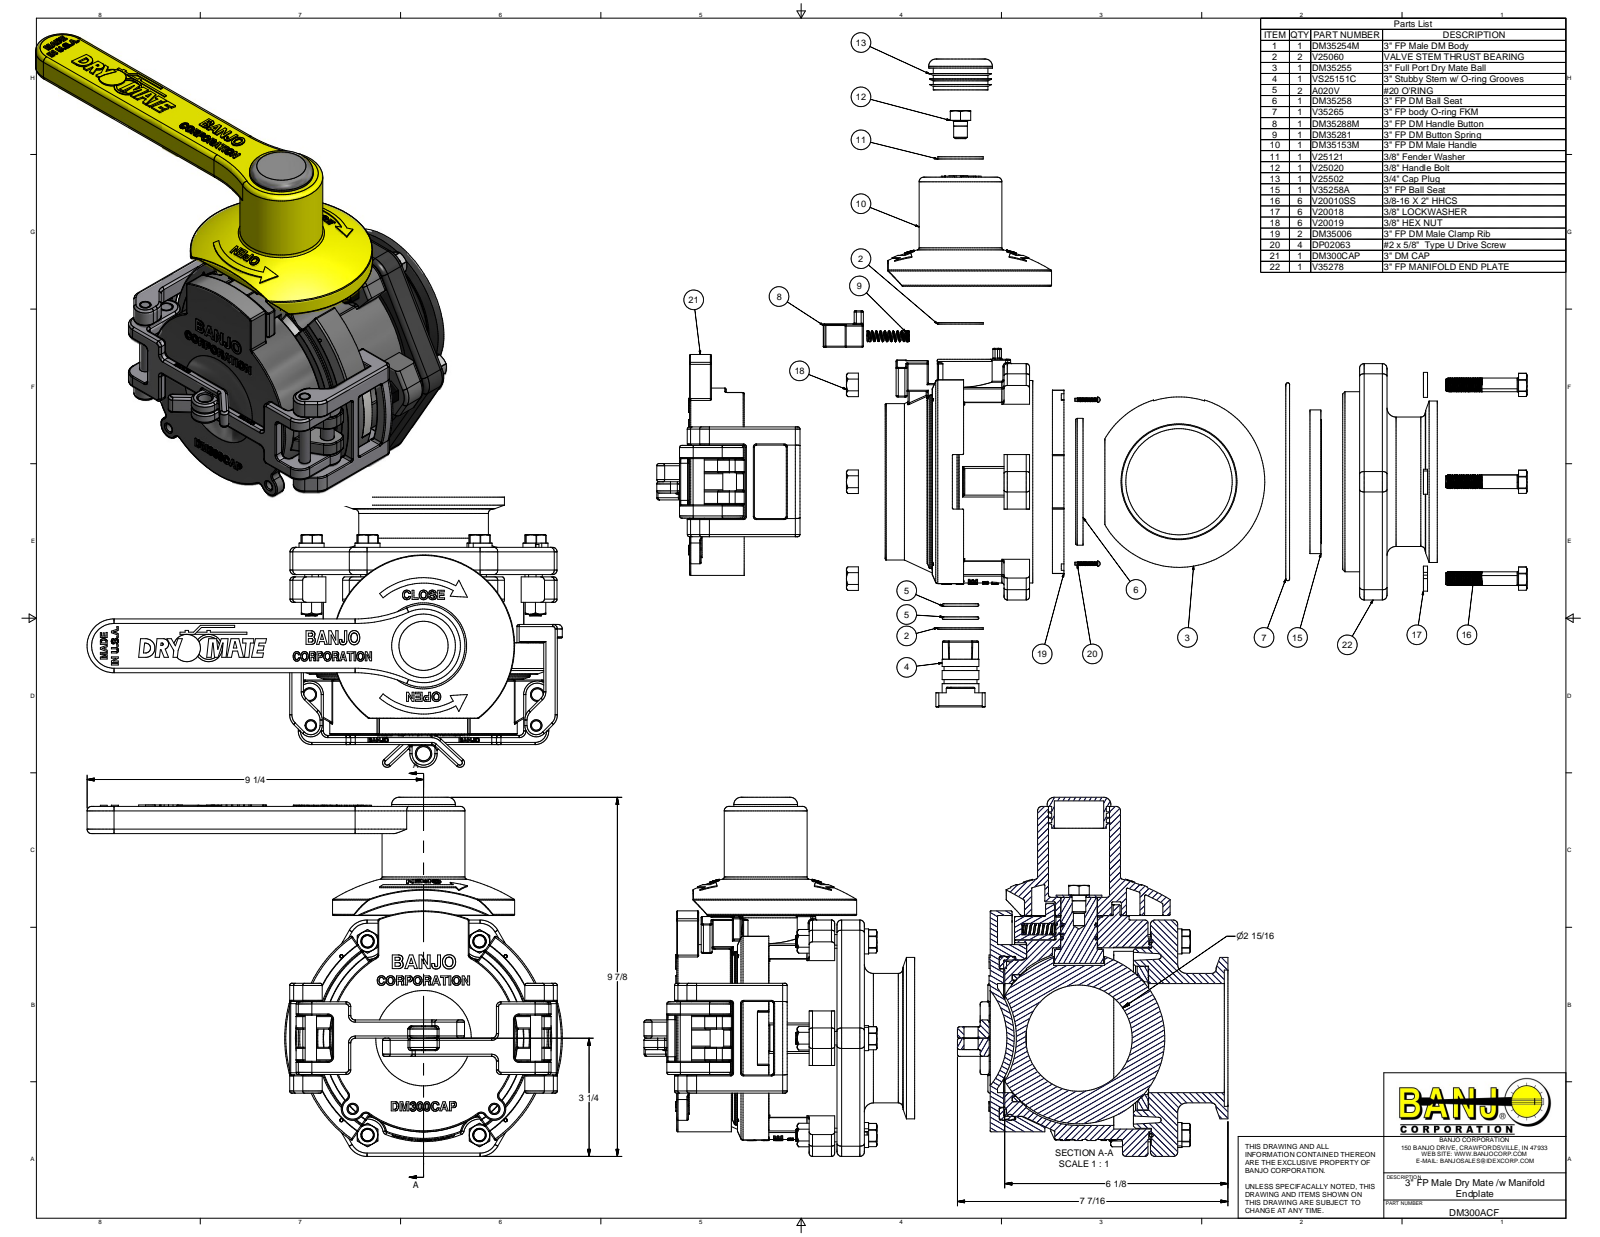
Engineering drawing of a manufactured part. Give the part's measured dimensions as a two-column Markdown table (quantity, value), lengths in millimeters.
| quantity | value |
| --- | --- |
| part name | DM35254MX; DM35254M; V35278X; V35278 (+8 more) |
| STEP written by | Autodesk Inventor 2014 (AUTOMOTIVE_DESIGN) |
| units | millimeters |
| bodies | 51 solids, 5496 faces (1702 planar, 1470 cylindrical, 2324 other) |
| overall size | 331.5 × 250.82 × 188.72 |
| volume | 2 180 000 mm³ |
| surface area | 597 304 mm² |
| round holes (diameter × count) | 7.81 × 6, 9.78 × 6, 11.18 × 6, 2.18 × 4, 3.17 × 4, 6.35 × 2, 8 × 2, 8.13 × 2, 9.52 × 2, 7.8 × 1, 7.95 × 1, 9.91 × 1 |
| round bosses / shafts (diameter × count) | 8.24 × 90, 9.52 × 7, 17.46 × 6, 2.08 × 4, 9.78 × 2, 8.25 × 2, 7.9 × 2, 141.48 × 1 |
| partial cylindrical surfaces (radius × count) | 0.76 × 272, 1.52 × 118, 3.17 × 40, 2.29 × 14, 9.53 × 14, 4.12 × 12, 0.25 × 10, 0.51 × 8 |
| main face-to-face distances | 130.81, 6.35, 18.41, 112.4, 19.43, 3.05, 106.05, 9.15, 54.23, 165.1 |
| hole center spacings | 78.1, 78.11, 135.28, 20.96, 60.93, 80.96, 96.86, 106.93 |
